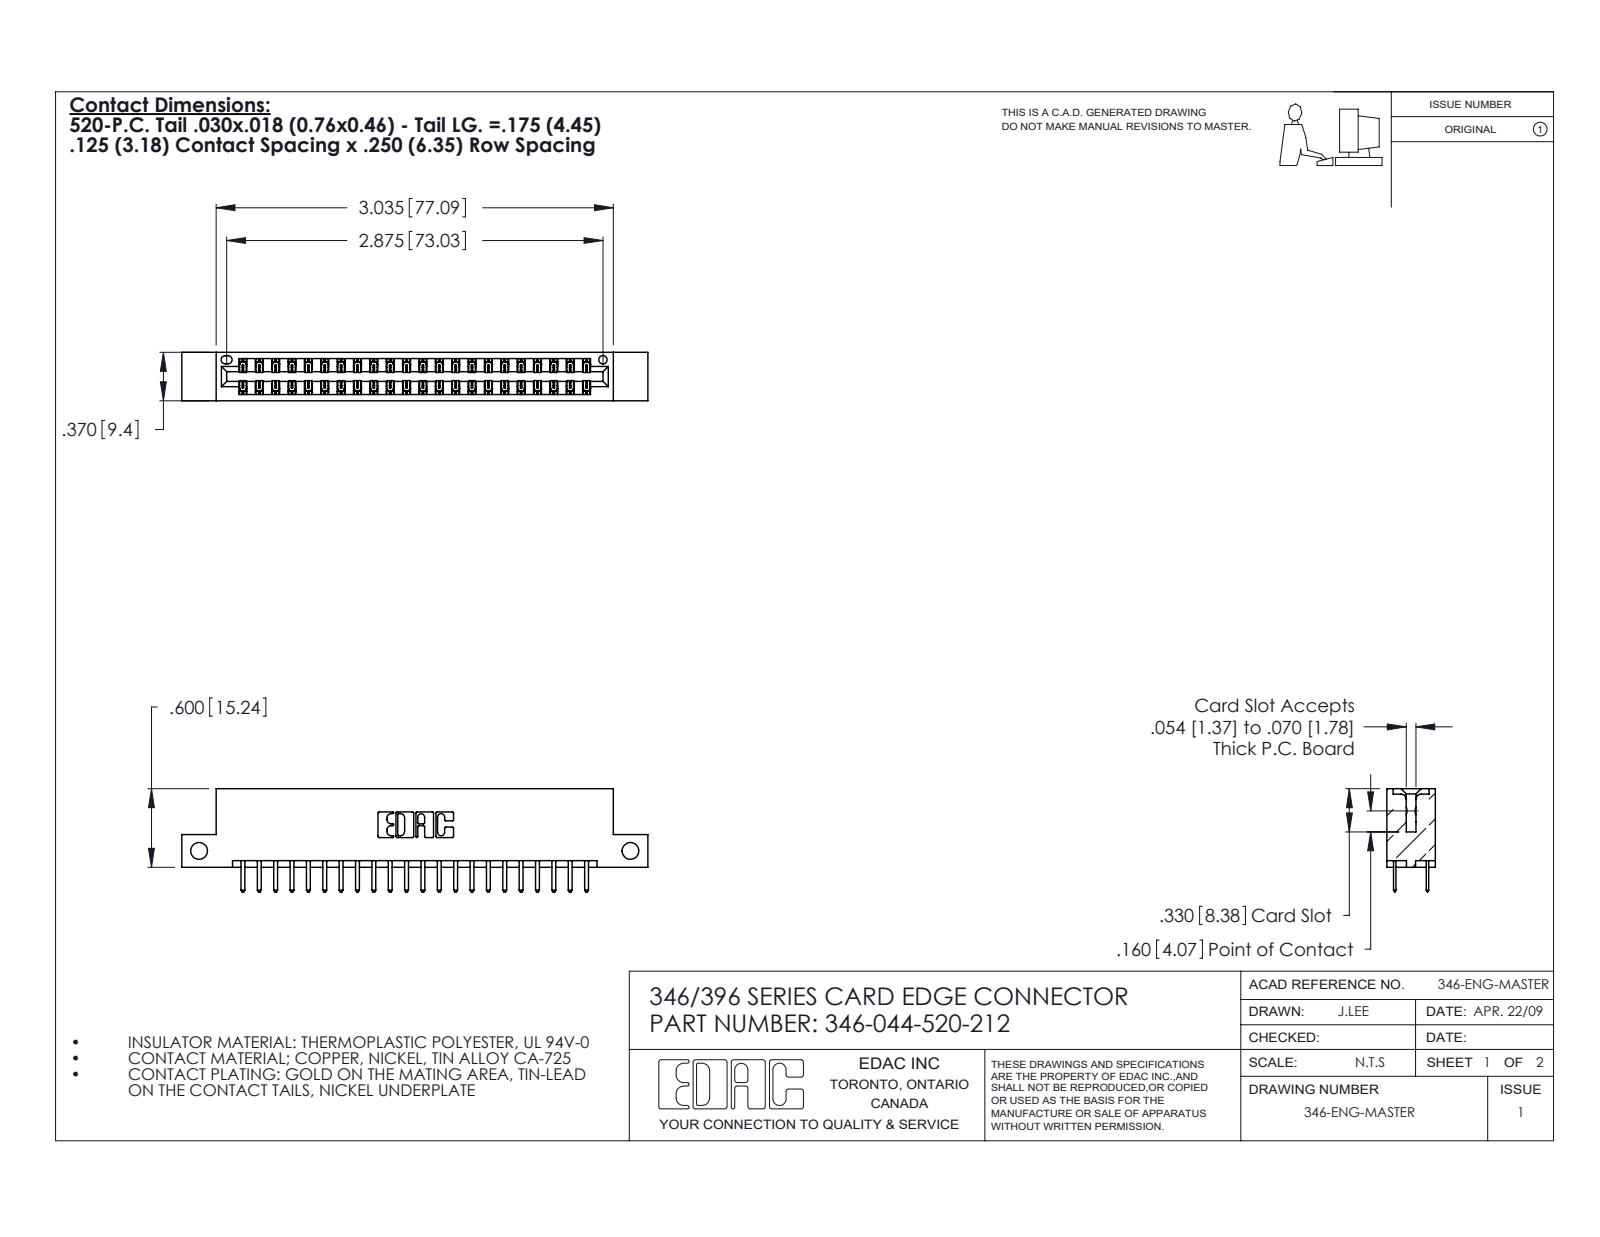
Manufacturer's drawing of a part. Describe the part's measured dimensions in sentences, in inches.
The part is named "346 Part_Flush Mounting Lugs - Side Mount; 346-044-520-212; 345-292-001_345-293-120". Its 3-D file was written by "SolidWorks 2020 (CONFIG_CONTROL_DESIGN)". It is 45 solids with 2586 faces: 1704 planar, 882 cylindrical and 0 other. Overall it measures 3.56 by 0.788 by 0.37 inches. Its volume is 0.522 cubic inches and its surface area 17.46 square inches. Round holes: 2 of diameter 0.128, 1 of diameter 0.064. Partial cylindrical surfaces (rounded edges, fillets, slot ends): 66 of radius 0.006, 48 of radius 0.01, 22 of radius 0.01, 6 of radius 0.007, 6 of radius 0.031, 3 of radius 0.026, 2 of radius 0.014, 2 of radius 0.022. The main face-to-face distances are 0.048, 0.322, 0.25, 0.37, 0.275, 0.072, 0.298, 0.025, 0.148, 0.222. The hole center spacings are 3.295.
